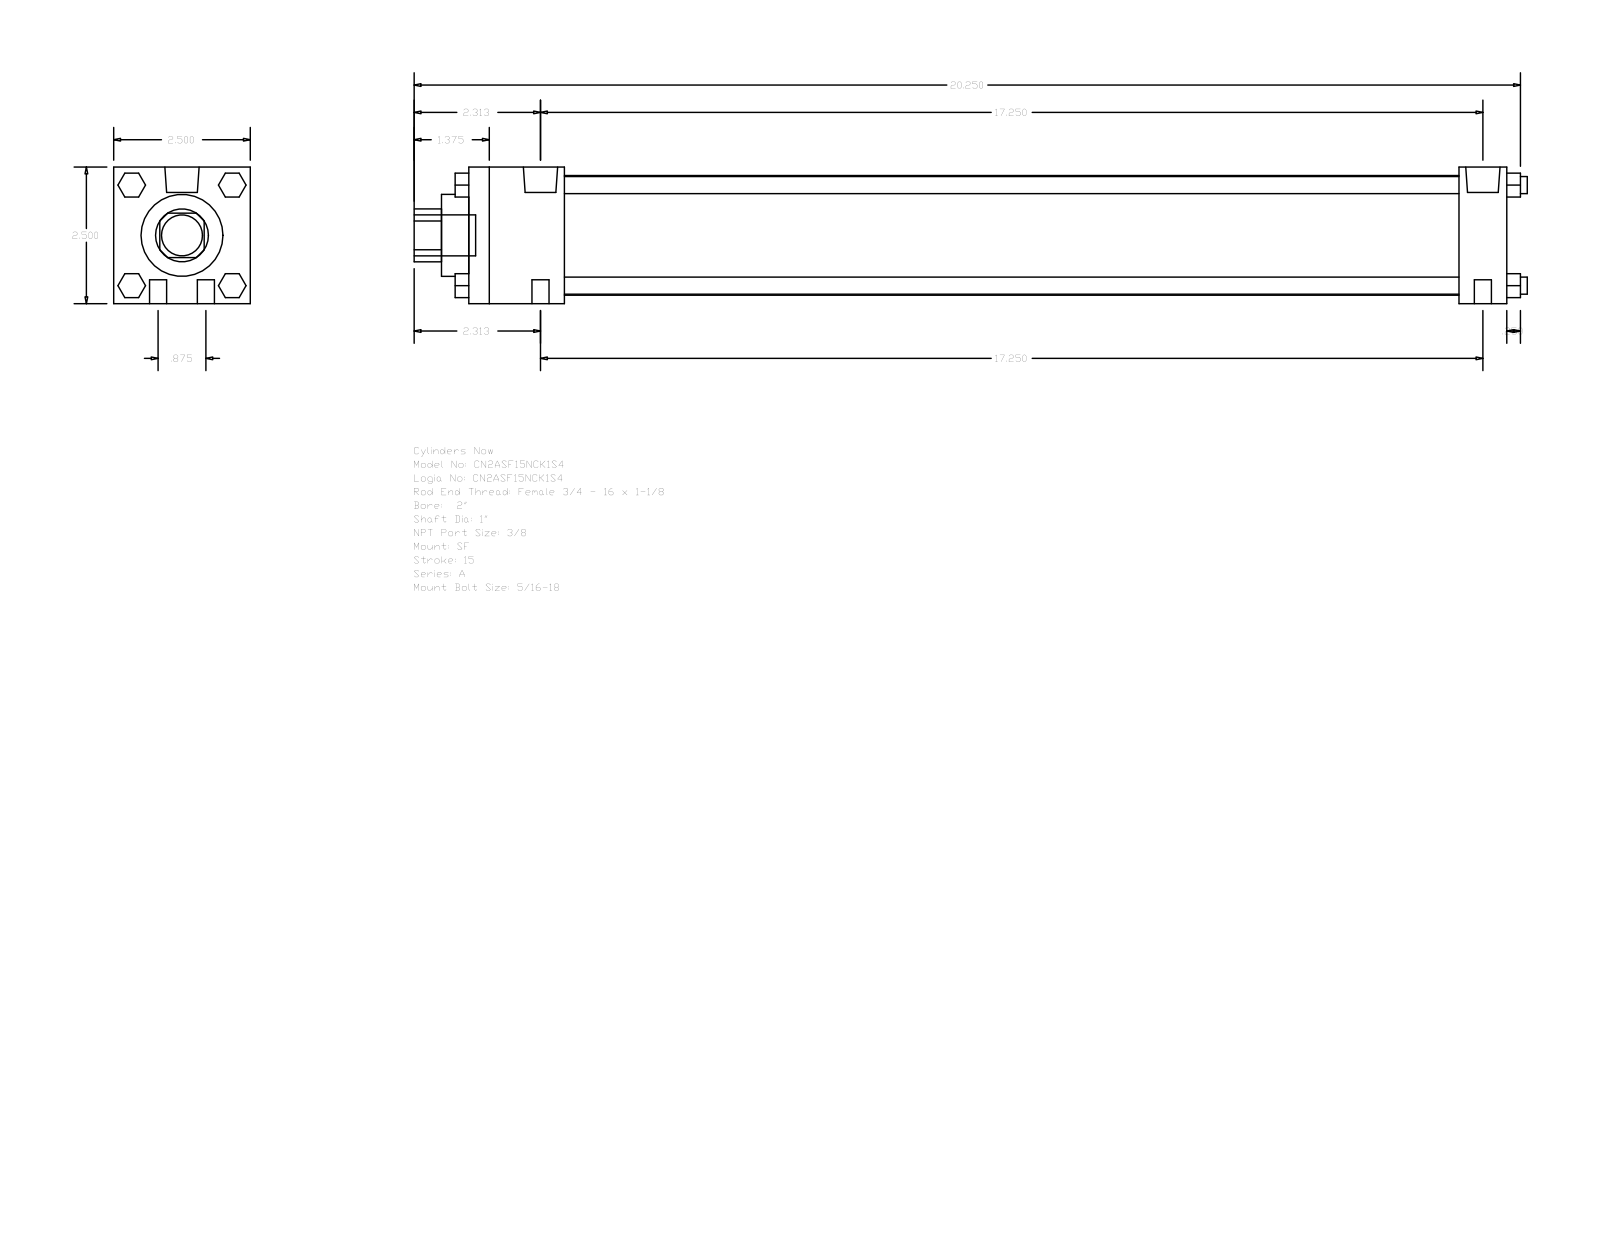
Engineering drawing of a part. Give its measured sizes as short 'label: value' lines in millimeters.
name: A_SF__0200_1
written by: GSSL Pune (CONFIG_CONTROL_DESIGN)
unit: mm
bodies: 0 solids, 124 faces (94 planar, 30 cylindrical, 0 other)
size: 517.52 × 63.5 × 63.5
holes: 1× ⌀25.4, 1× ⌀38.1, 1× ⌀55.63
bosses: 8× ⌀7.94, 2× ⌀15.93, 2× ⌀5.56, 1× ⌀19.05
rounds: 1× R12.29
face distances: 63.5, 482.6, 460.37, 22.23, 44.45, 415.92, 438.15, 12.7, 495.3, 6.35
